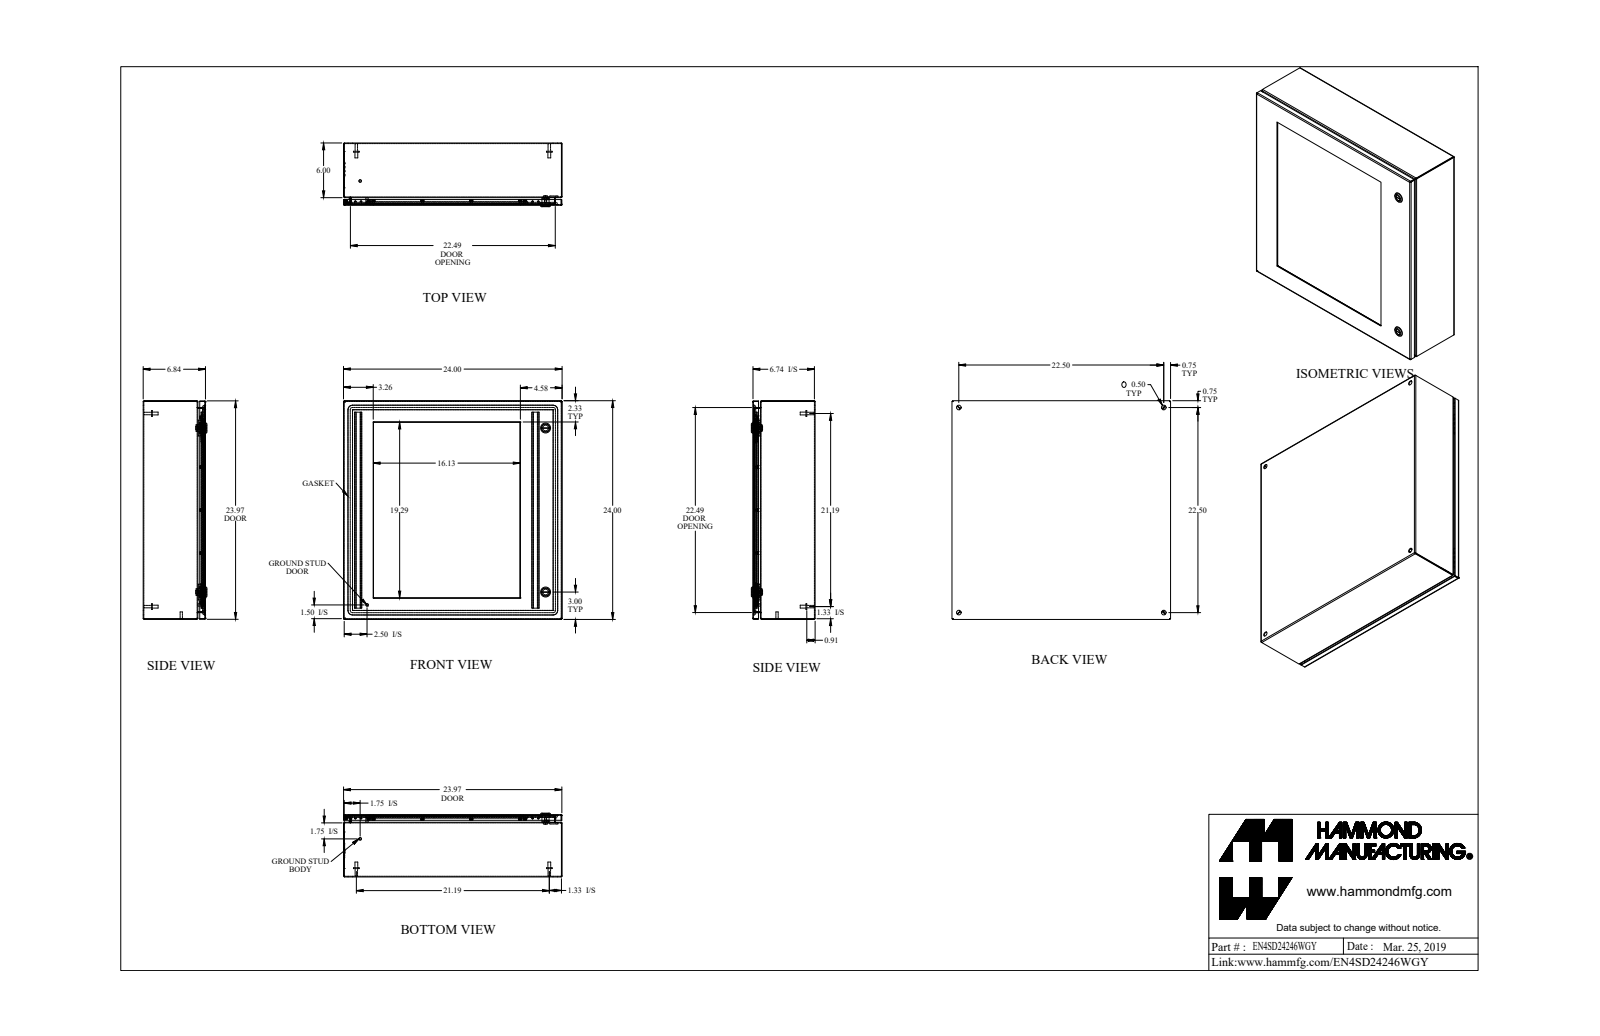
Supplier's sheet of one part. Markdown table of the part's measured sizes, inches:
| quantity | value |
| --- | --- |
| part name | EN4SD24246WGY_Default |
| STEP written by | SolidWorks 2019 (CONFIG_CONTROL_DESIGN) |
| units | inches |
| bodies | 72 solids, 1482 faces (763 planar, 453 cylindrical, 266 other) |
| overall size | 24 × 24 × 6.997 |
| volume | 217 in³ |
| surface area | 4 501 in² |
| round holes (diameter × count) | 0.13 × 18, 0.25 × 18, 0.5 × 4, 0.232 × 2, 0.625 × 2, 0.785 × 2, 0.172 × 1, 0.24 × 1, 0.242 × 1 |
| round bosses / shafts (diameter × count) | 0.226 × 19, 0.368 × 18, 0.164 × 18, 0.625 × 4, 0.313 × 4, 0.27 × 4, 1.1 × 2, 0.525 × 2 |
| partial cylindrical surfaces (radius × count) | 0.036 × 20, 0.108 × 20, 0.043 × 12, 0.081 × 12, 0.125 × 12, 0.382 × 12, 19.003 × 8, 0.006 × 4 |
| main face-to-face distances | 0.072, 6.765, 6.693, 23.928, 6.443, 0.25, 6.515, 0.322, 23.856, 24 |
| hole center spacings | 4.719, 17.781, 14.156, 18.875, 19.57, 21.03, 5.372, 5.372 |
